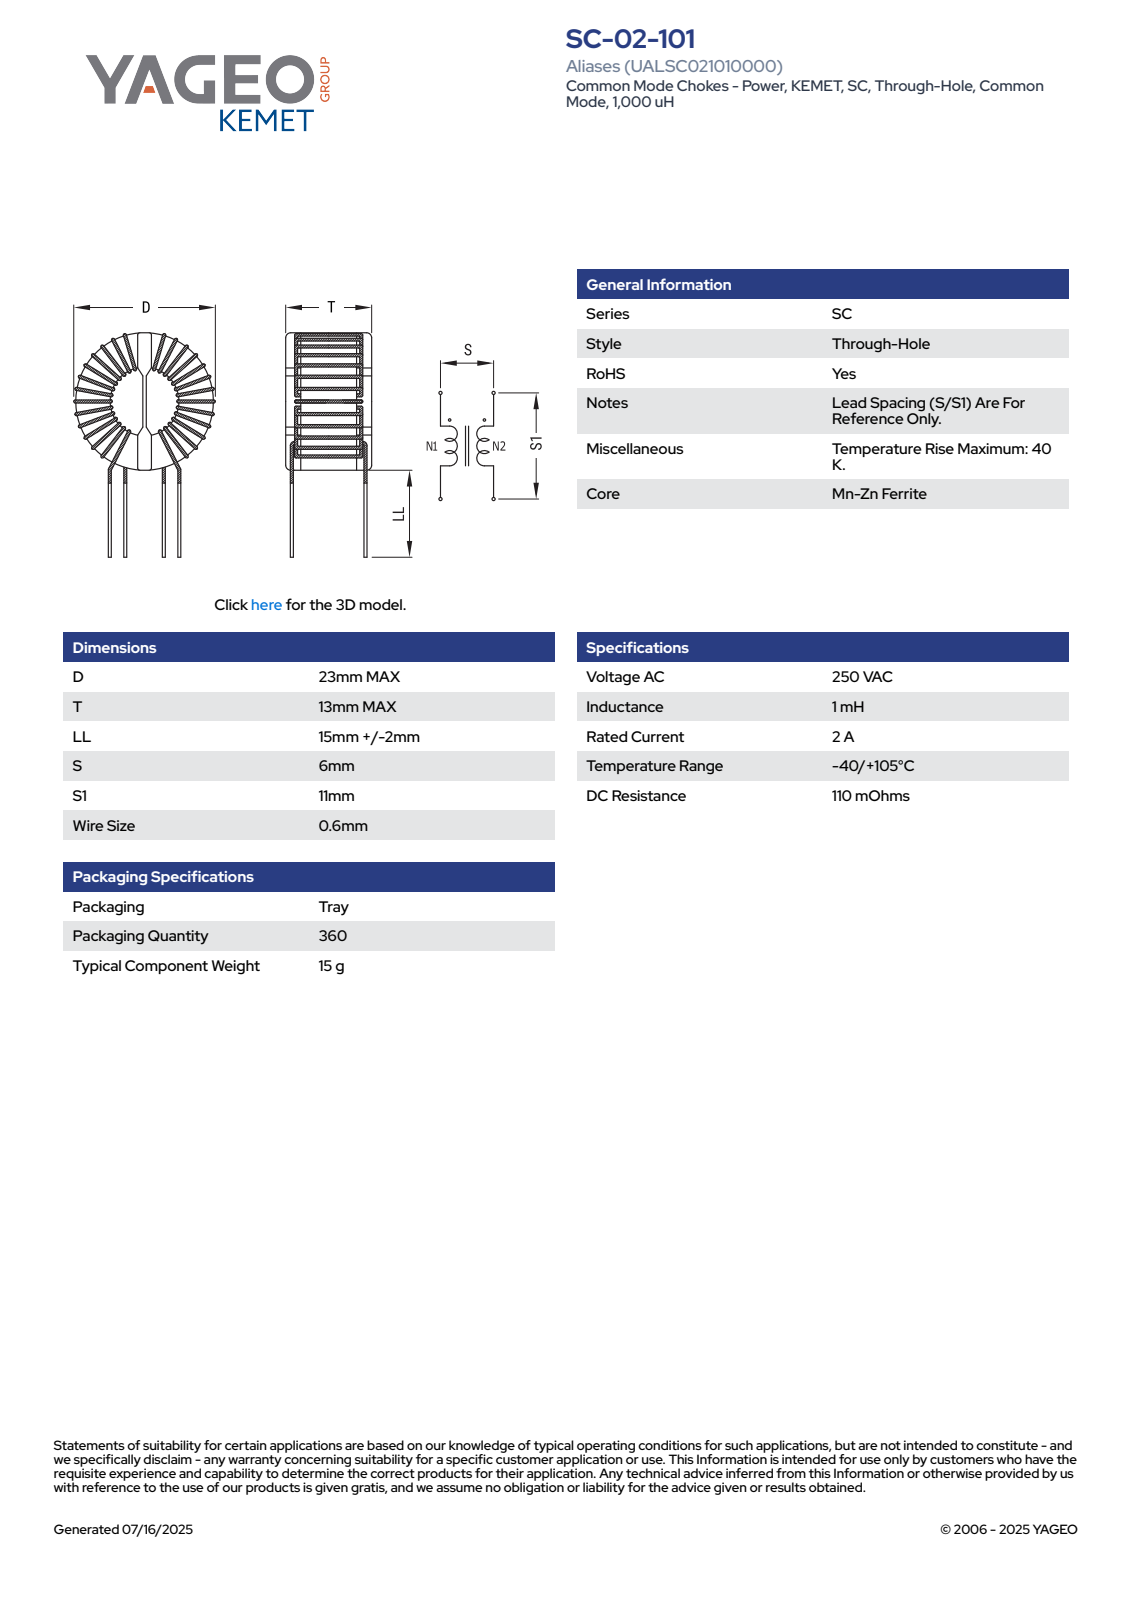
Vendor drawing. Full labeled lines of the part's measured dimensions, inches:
Part name (STEP PRODUCT): SC-02-101
STEP written by: SolidWorks 2018 (AUTOMOTIVE_DESIGN)
Units: inches
Bodies: 1 solid, 276 faces (115 planar, 81 cylindrical, 80 other)
Overall size (bounding box): 1.433 × 0.906 × 0.512
Volume: 0.223 in³ · Surface area: 3.954 in²
Round bosses / shafts (diameter × count): ⌀0.024 ×8
Partial cylindrical surfaces — rounded edges, fillets, slot ends (radius × count): R0.012 ×16, R0.008 ×4, R0.112 ×1, R0.194 ×1, R0.213 ×1, R0.217 ×1, R0.218 ×1, R0.371 ×1
Main face-to-face distances: 0.394, 0.079, 0.047, 0.031, 0.059, 0.126, 0.453, 0.114, 0.055, 0.398
